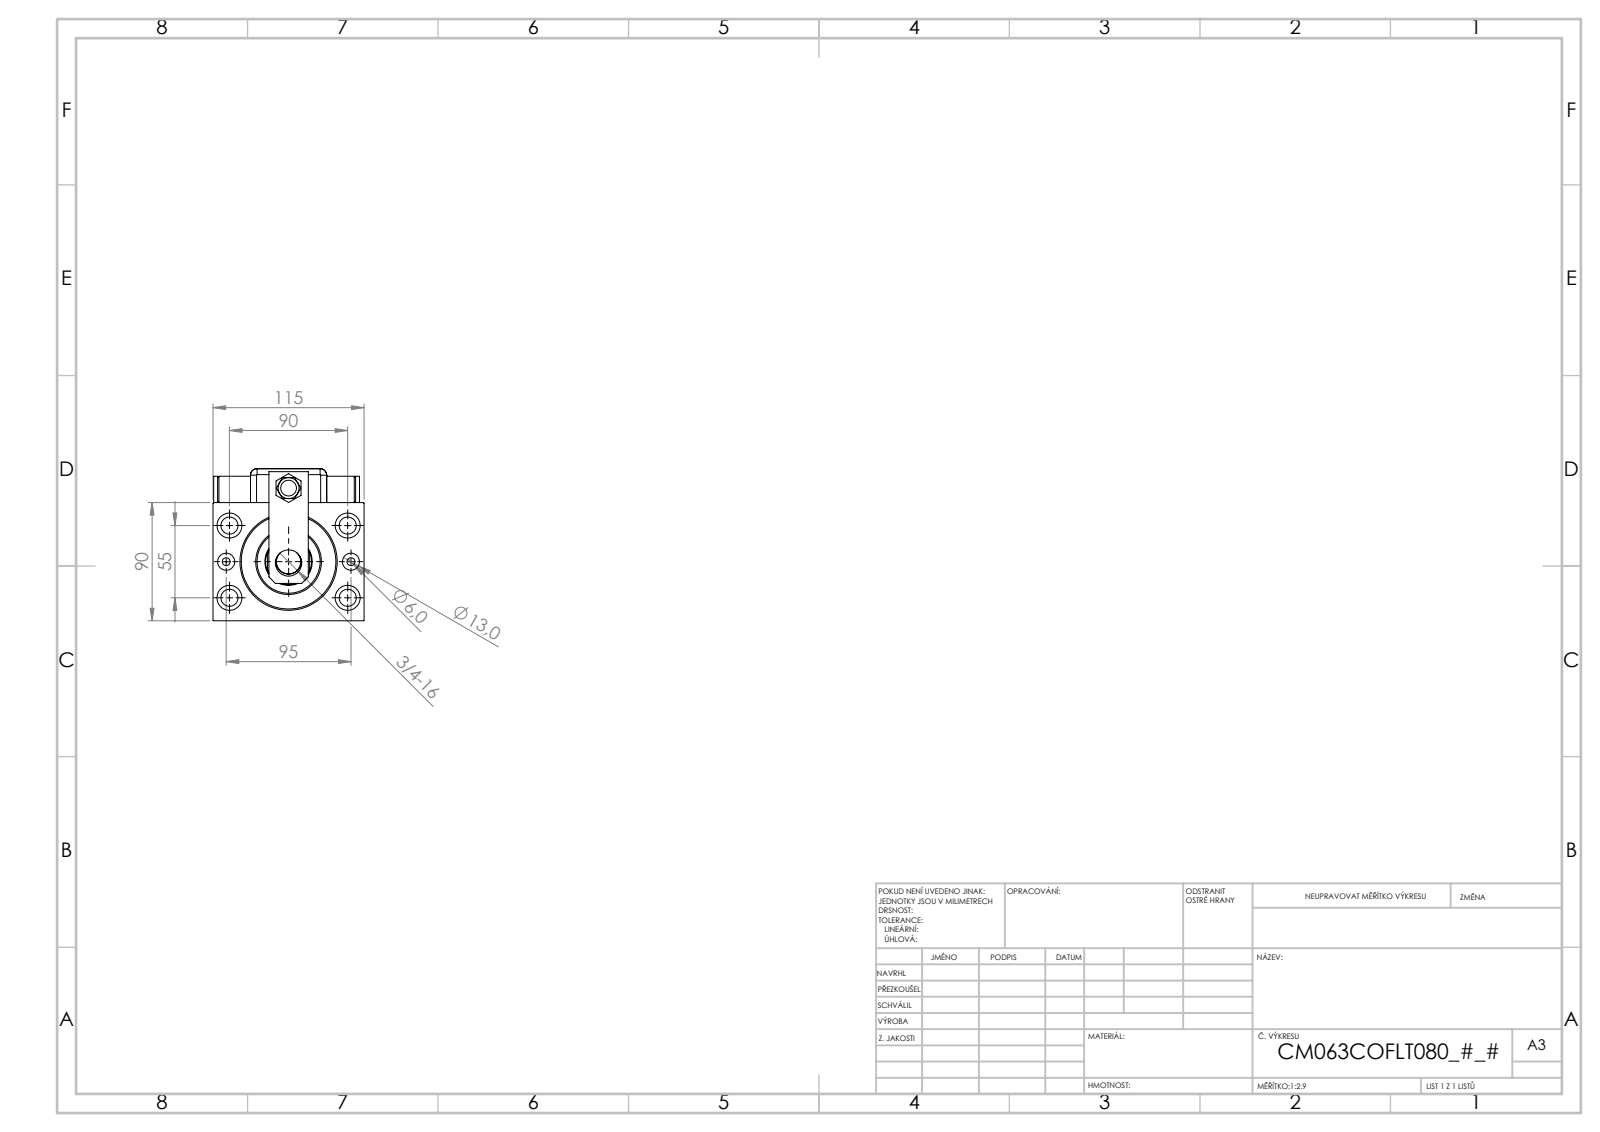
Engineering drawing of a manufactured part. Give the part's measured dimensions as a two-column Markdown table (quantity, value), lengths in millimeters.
| quantity | value |
| --- | --- |
| part name | SWITCH DIM A_G; MAGNETIC SWITCH Q; ZARAZKA_Q; KRYT (+7 more) |
| STEP written by | SolidWorks 2019 (CONFIG_CONTROL_DESIGN) |
| units | millimeters |
| bodies | 13 solids, 1242 faces (614 planar, 111 cylindrical, 517 other) |
| overall size | 210.46 × 115.8 × 115 |
| volume | 1 538 000 mm³ |
| surface area | 255 838 mm² |
| round holes (diameter × count) | 13 × 7, 19 × 4, 4 × 2, 6 × 2, 8 × 2, 12 × 1, 14 × 1, 18.5 × 1, 20 × 1, 36 × 1, 63 × 1, 65 × 1 |
| round bosses / shafts (diameter × count) | 20 × 3, 16 × 2, 14 × 2, 6 × 2, 50 × 1 |
| partial cylindrical surfaces (radius × count) | 5 × 9, 10 × 1, 17.5 × 1 |
| main face-to-face distances | 90, 115, 3, 158, 25.8, 115.8, 17.5, 140.5, 28.5, 112.8 |
| hole center spacings | 27.61, 52.74, 53.27, 96.5, 47.5, 47.51, 52.22, 55 |
